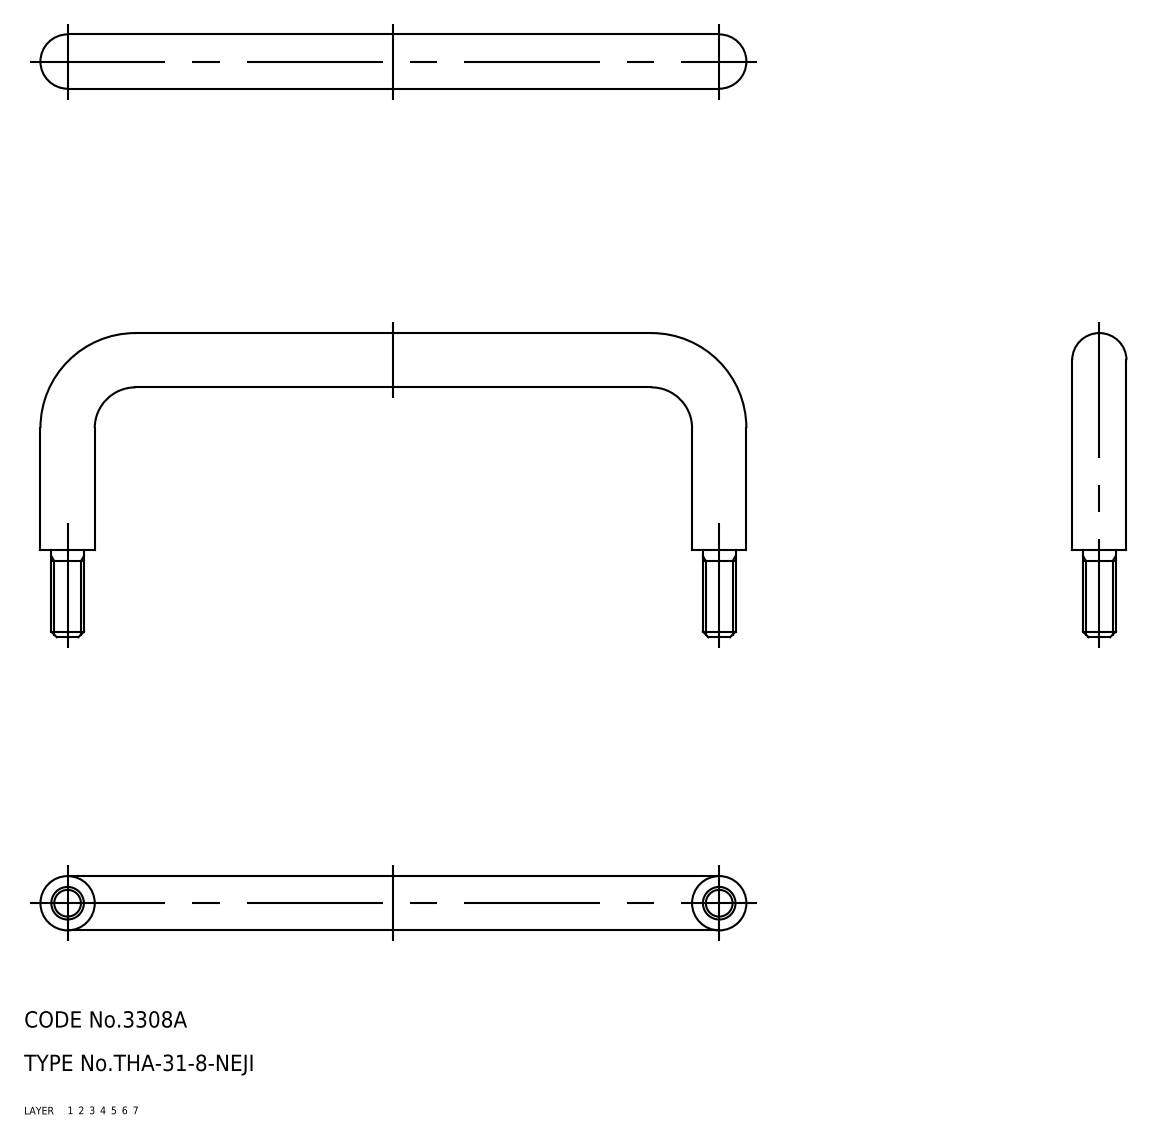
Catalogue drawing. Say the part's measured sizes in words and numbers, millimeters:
The part is named "pull". Its 3-D file was written by "CADfix (AUTOMOTIVE_DESIGN)". It is 1 solid with 22 faces: 0 planar, 0 cylindrical and 22 other. Overall it measures 130 by 56 by 10 millimeters. Its volume is 15 022 cubic millimeters and its surface area 6 370 square millimeters.
